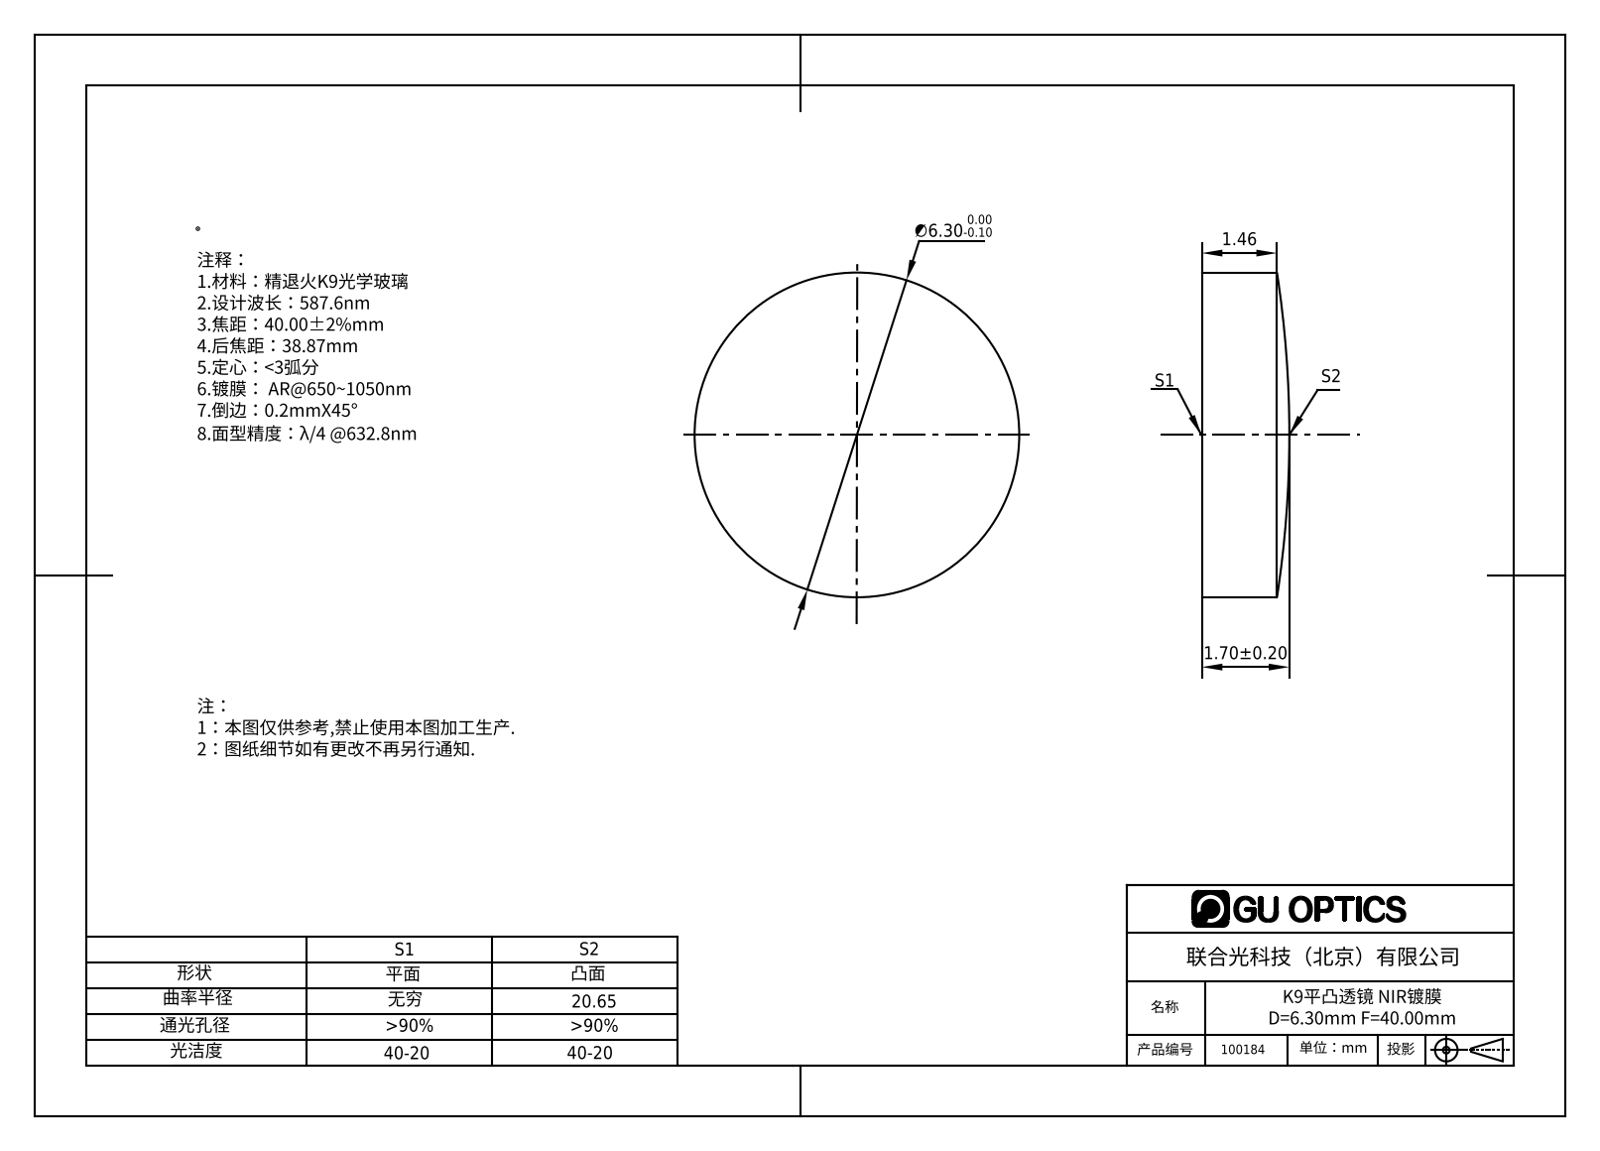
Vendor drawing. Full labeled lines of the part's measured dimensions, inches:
Part name (STEP PRODUCT): 100184
STEP written by: SolidWorks 2016 (AUTOMOTIVE_DESIGN)
Units: inches
Bodies: 1 solid, 5 faces (1 planar, 2 cylindrical, 2 other)
Overall size (bounding box): 0.248 × 0.248 × 0.067
Volume: 0.003 in³ · Surface area: 0.14 in²
Round bosses / shafts (diameter × count): ⌀0.248 ×1
